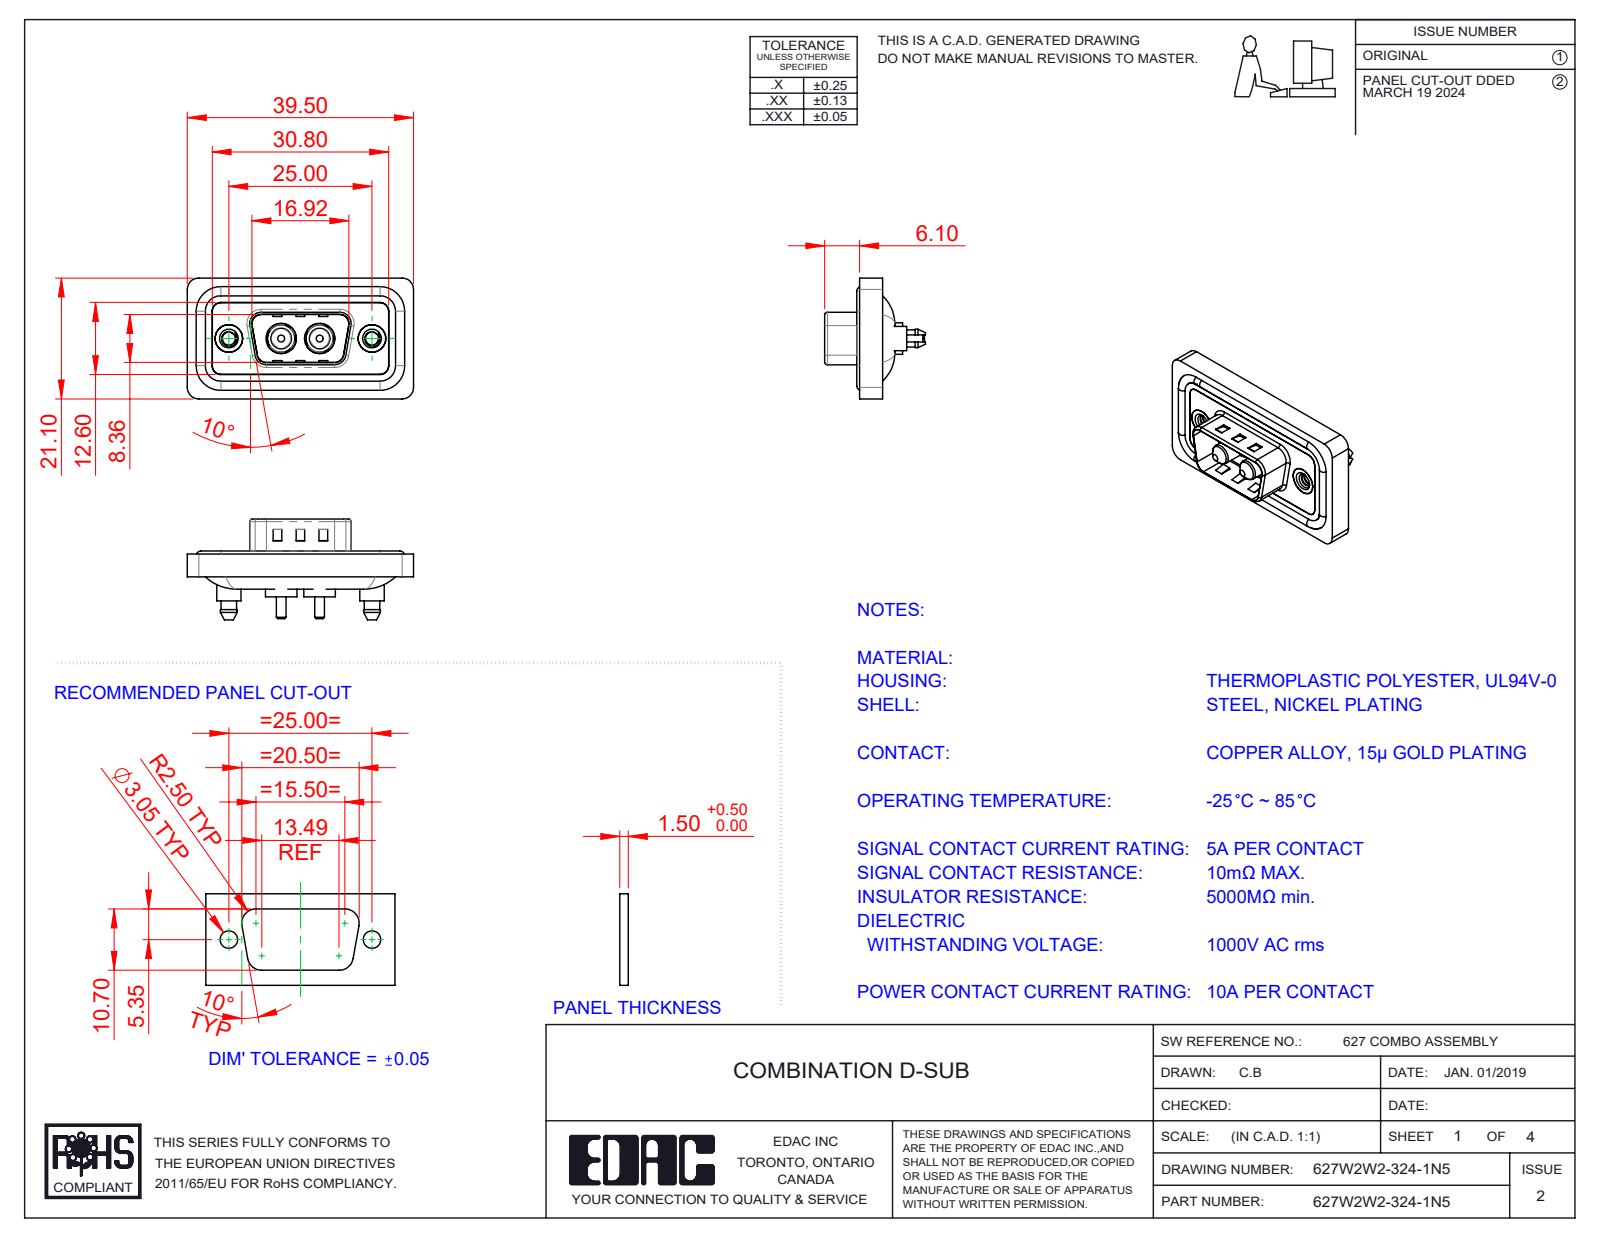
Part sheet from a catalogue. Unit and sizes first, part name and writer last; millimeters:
Units: millimetres
Overall size (bounding box): 39.5 × 21.1 × 17.6
Round holes (diameter × count): ⌀2.26 ×2, ⌀4 ×2, ⌀4.8 ×2, ⌀4.85 ×2, ⌀5 ×2, ⌀5.3 ×2
Round bosses / shafts (diameter × count): ⌀1.6 ×4, ⌀5.5 ×2, ⌀5.4 ×2, ⌀5.2 ×2, ⌀4.9 ×2, ⌀4.75 ×2, ⌀4.25 ×2, ⌀3.75 ×2
Partial cylindrical surfaces — rounded edges, fillets, slot ends (radius × count): R1.5 ×24, R2 ×18, R1.6 ×10, R0.5 ×8, R0.25 ×4, R0.6 ×4, R0.65 ×4, R0.9 ×4
Main face-to-face distances: 0.4, 1.1, 2.9, 1.5, 3.1, 0.5, 1.6, 4, 0.7, 2.5
Hole centre spacings: 9.14, 15.86, 6.72, 25
Volume: 4 565 mm³ · Surface area: 7 292 mm²
Bodies: 11 solids, 539 faces (181 planar, 250 cylindrical, 108 other)
Part name (STEP PRODUCT): 627Combo Shell Rear_09 Contacts; 627W2W2-324-1N5; 627Combo Threaded Boardlock_5; 627Combo Waterproof Housing_09 Contacts (+3 more)
STEP written by: SolidWorks 2023 (CONFIG_CONTROL_DESIGN)
